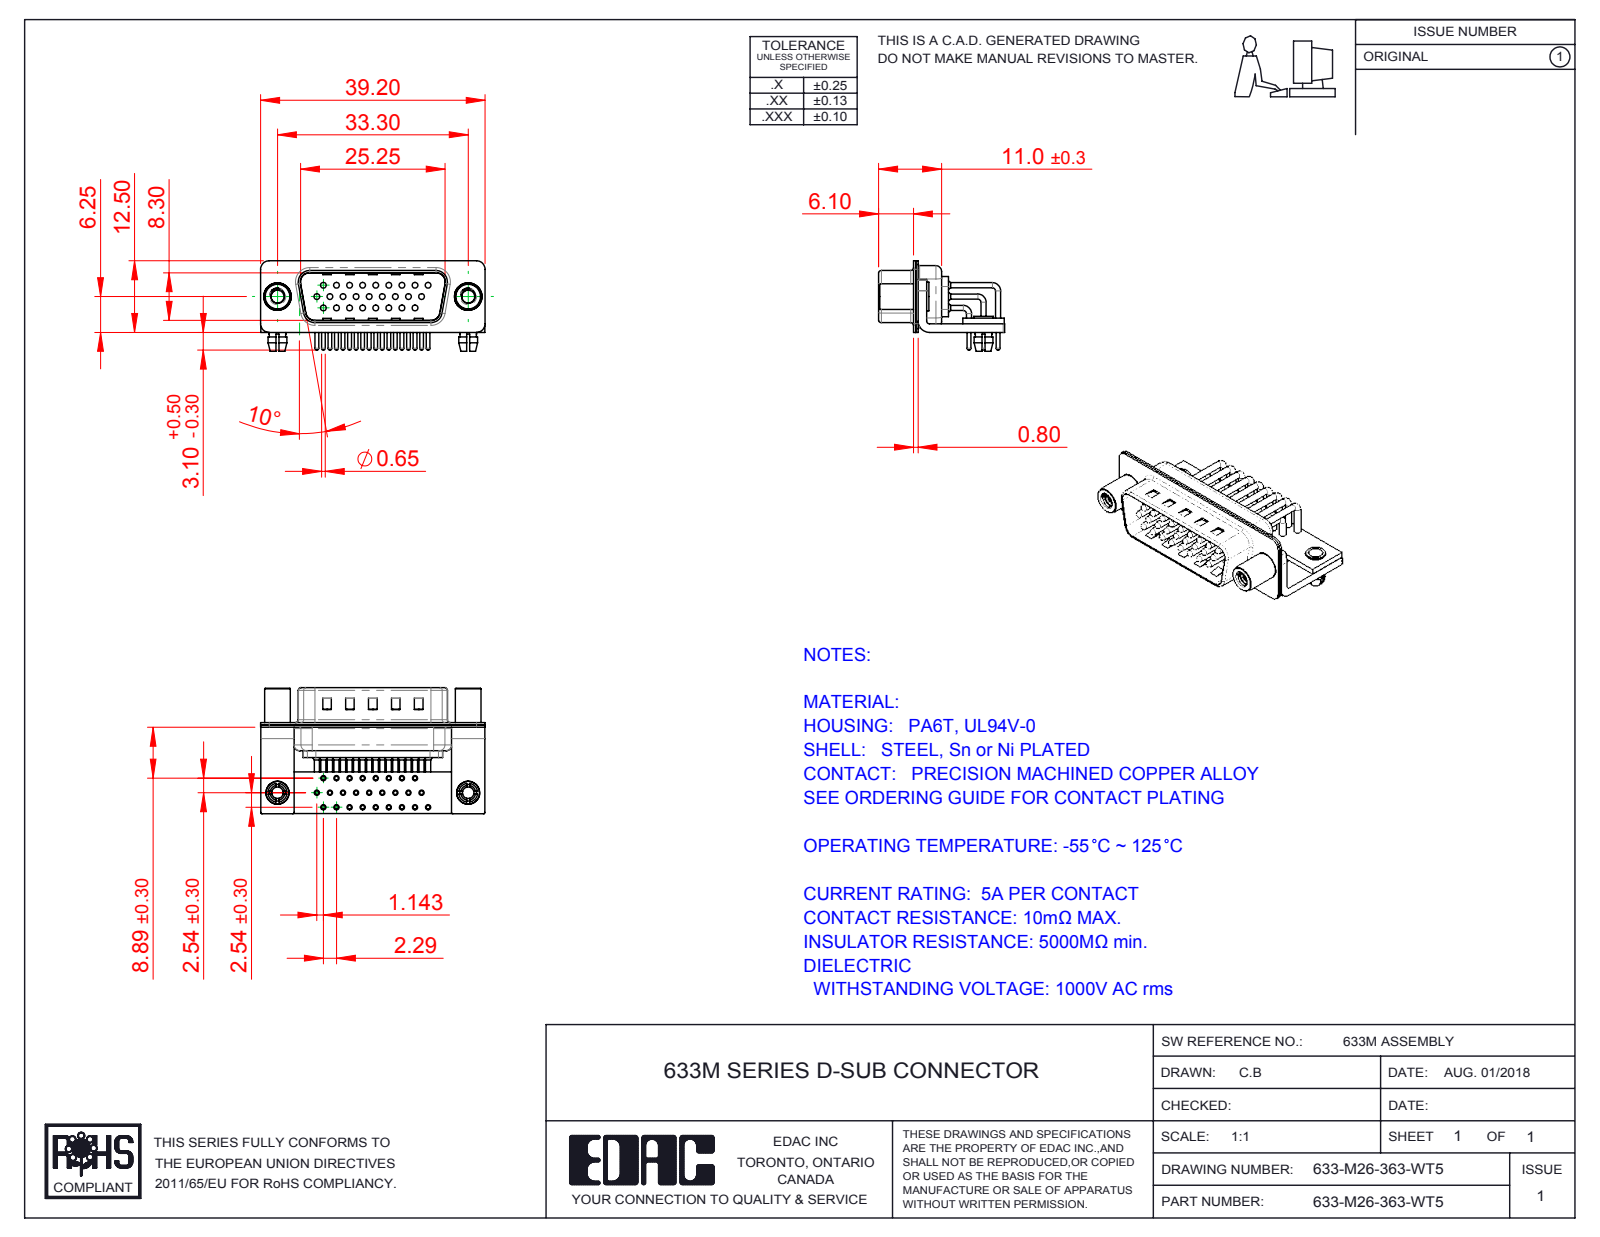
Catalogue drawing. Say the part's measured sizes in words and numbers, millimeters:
The part is named "633M Housing_26 Contacts; 633M 4-40 Threaded Standoff; 633M Stabilizer Board_26 Contacts; 633M Contact Row 2 (+7 more)". Its 3-D file was written by "SolidWorks 2016 (CONFIG_CONTROL_DESIGN)". It is 36 solids with 3444 faces: 1879 planar, 1217 cylindrical and 348 other. Overall it measures 39.2 by 22 by 15.8 millimeters. Its volume is 2 794 cubic millimeters and its surface area 8 558 square millimeters. Round holes: 28 of diameter 2, 26 of diameter 0.9, 26 of diameter 1, 26 of diameter 1.7, 2 of diameter 2.26, 2 of diameter 2.5, 2 of diameter 3.2, 2 of diameter 4, 2 of diameter 4.8. Round bosses or shafts: 26 of diameter 1.5, 26 of diameter 0.9, 26 of diameter 0.65, 2 of diameter 5, 2 of diameter 4.9, 2 of diameter 4.5, 2 of diameter 4, 2 of diameter 3.4. Partial cylindrical surfaces (rounded edges, fillets, slot ends): 26 of radius 1.01, 16 of radius 0.25, 16 of radius 1.5, 13 of radius 2, 9 of radius 0.5, 8 of radius 1.6, 4 of radius 0.6, 4 of radius 0.65. The main face-to-face distances are 0.4, 1.5, 0.85, 0.8, 1, 1.25, 1.9, 10.4, 9.55, 2.5. The hole center spacings are 4.57, 2.29, 2.28, 3.96, 6.86, 4.27, 6.05, 2.78.
